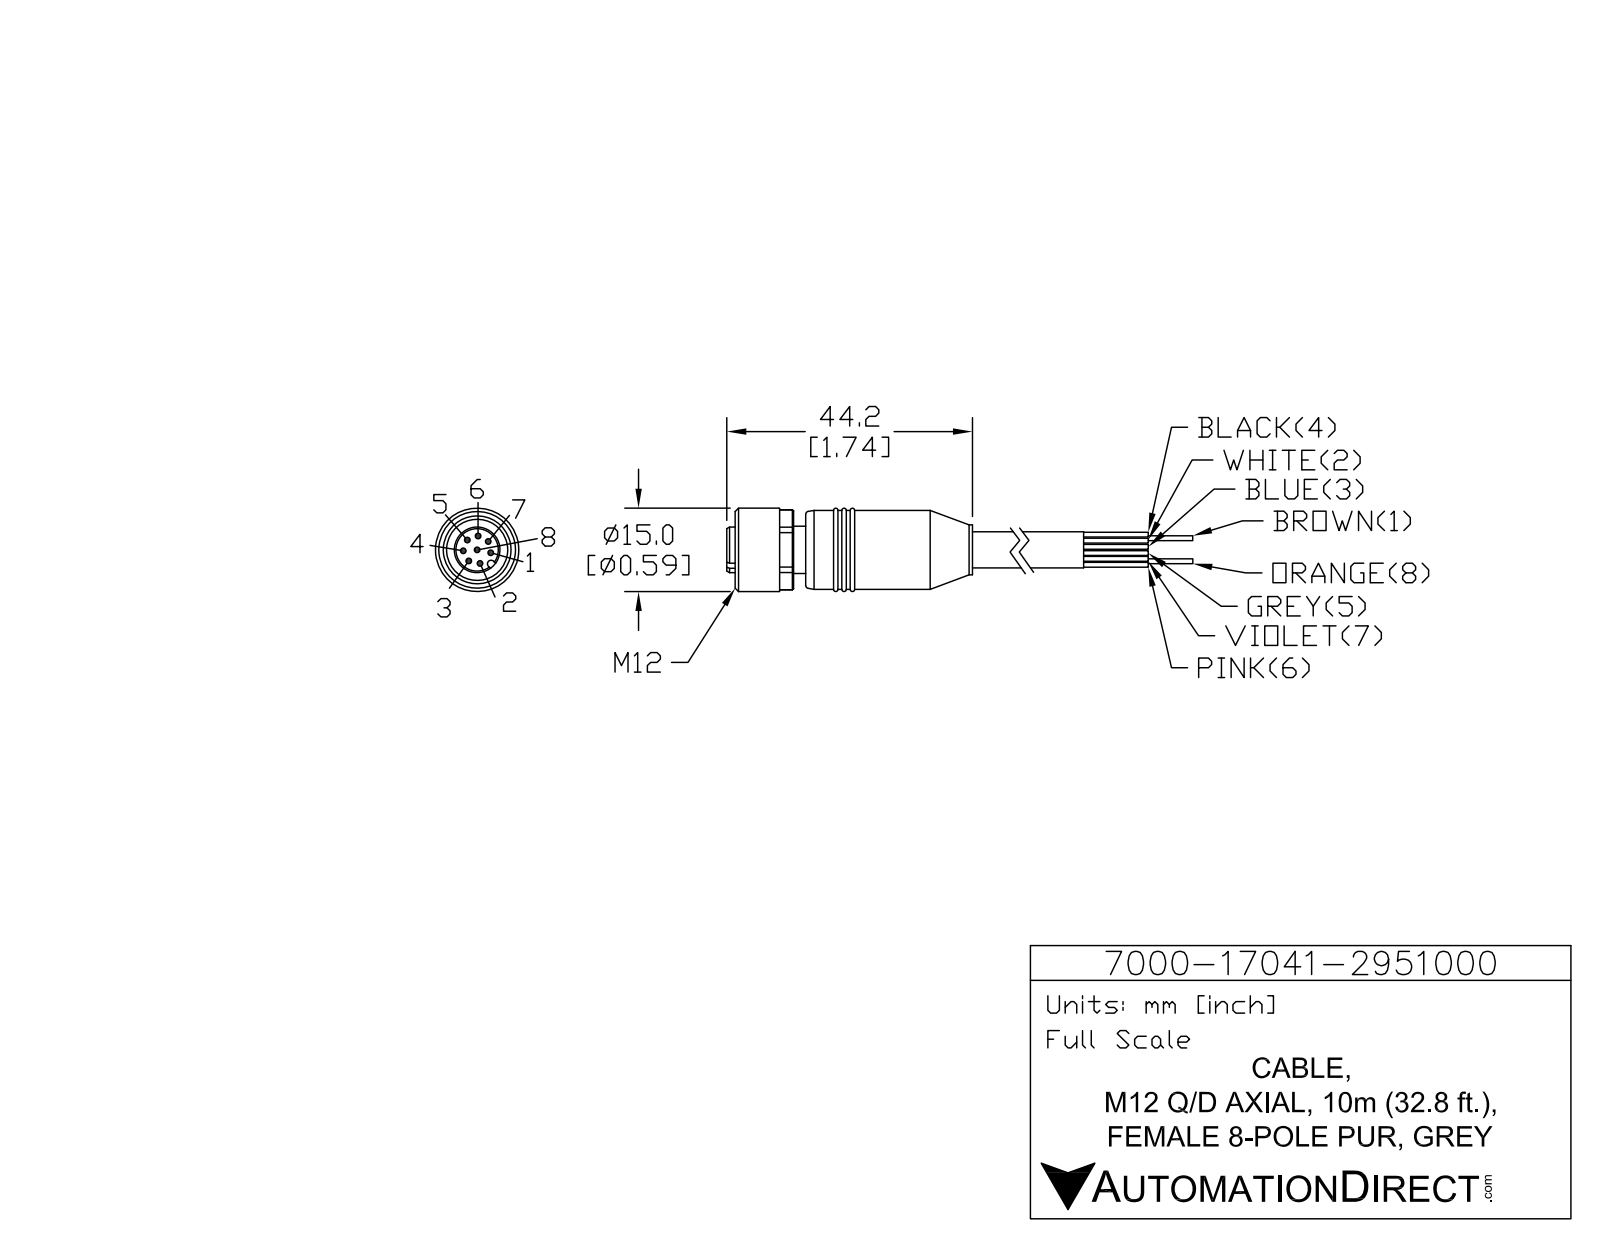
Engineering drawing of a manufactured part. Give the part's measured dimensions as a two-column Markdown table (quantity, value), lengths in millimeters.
| quantity | value |
| --- | --- |
| part name | 7000-17041-2951000 |
| STEP written by | SolidWorks 2015 (AUTOMOTIVE_DESIGN) |
| units | millimeters |
| bodies | 1 solid, 103 faces (31 planar, 44 cylindrical, 28 other) |
| overall size | 64.2 × 15 × 15 |
| volume | 6 618 mm³ |
| surface area | 3 393 mm² |
| round holes (diameter × count) | 1 × 8, 11 × 1 |
| round bosses / shafts (diameter × count) | 15 × 1, 14.2 × 1, 9 × 1, 8.5 × 1, 8.2 × 1, 6.5 × 1 |
| partial cylindrical surfaces (radius × count) | 0.65 × 1, 7.2 × 1 |
| main face-to-face distances | 2.2, 13, 3, 5.2, 9, 12, 14.2, 64.2, 55.2, 52.2 |
| hole center spacings | 2.5, 2.07, 3.78, 4.95, 2.08, 4.22, 4.79, 4.8 |
